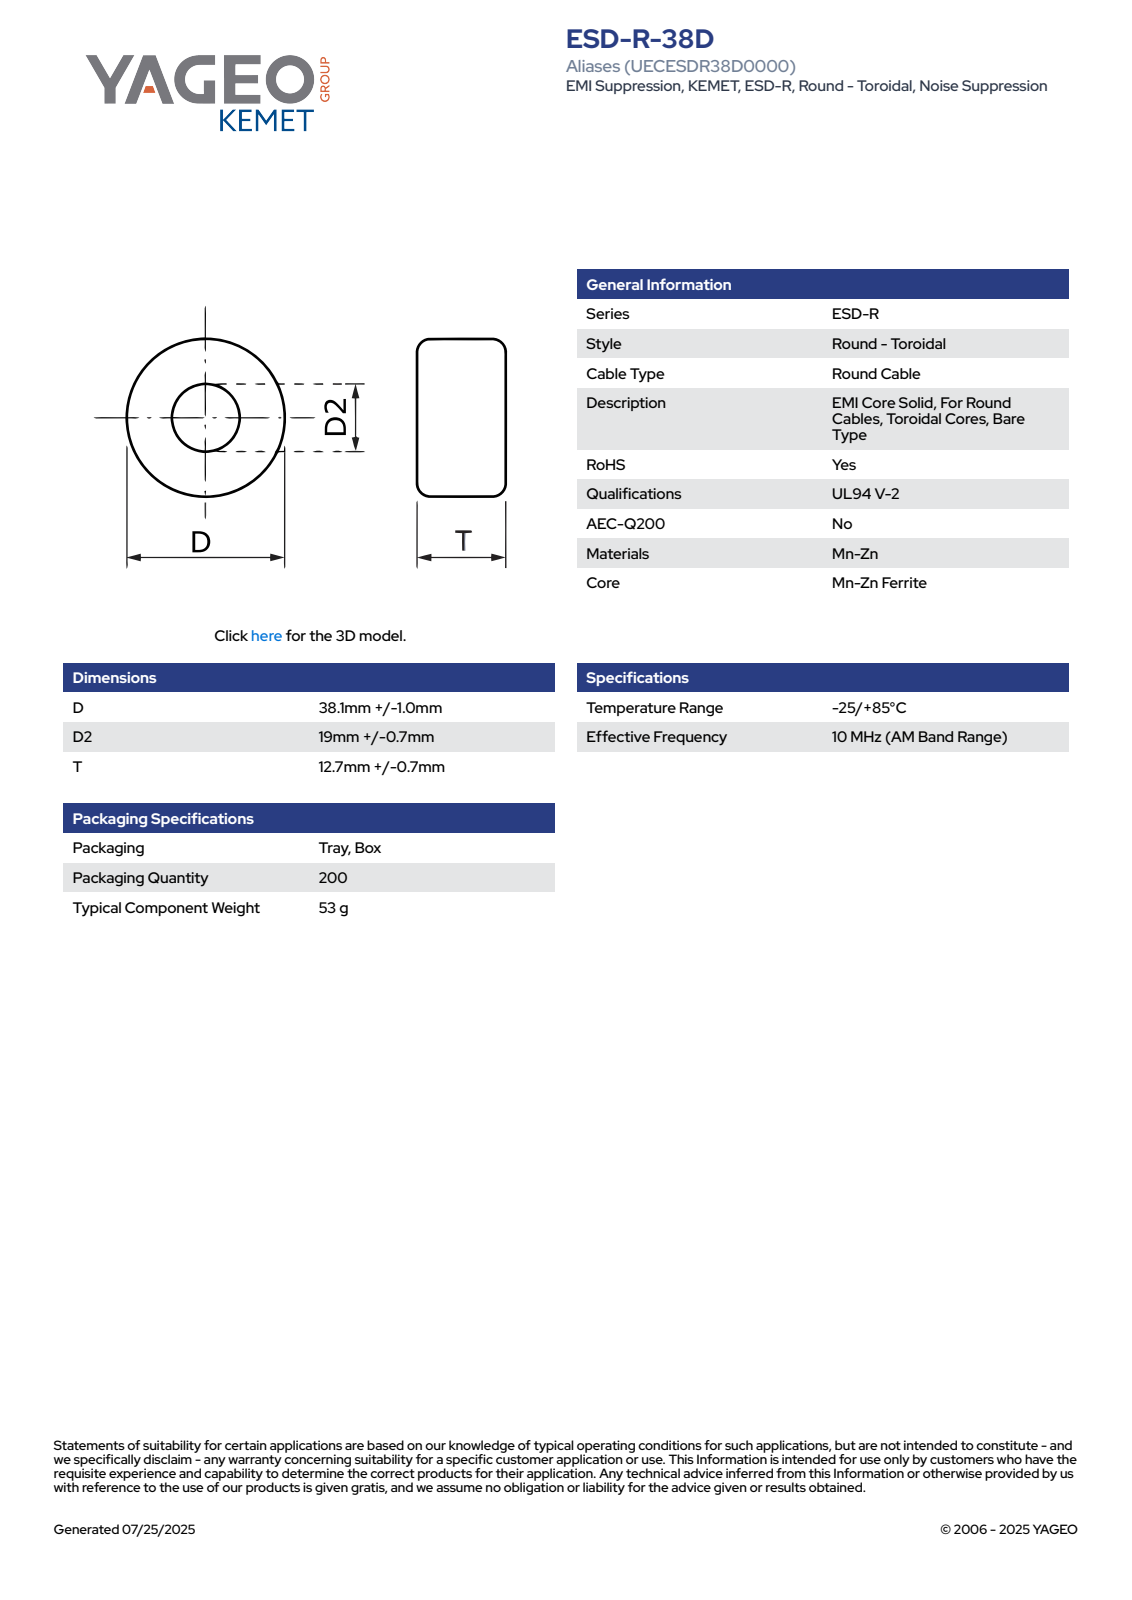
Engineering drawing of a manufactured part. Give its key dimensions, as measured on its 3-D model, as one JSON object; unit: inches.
{"part_name": "EC_KBC_D39.1D219T13.4", "step_written_by": "SolidWorks 2021 (AUTOMOTIVE_DESIGN)", "units": "inches", "bodies": {"solids": 1, "faces": 66, "planar": 24, "cylindrical": 7, "other": 35}, "overall_size": [1.54, 1.539, 0.528], "volume_in3": 0.745, "surface_area_in2": 6.453, "round_holes": [[0.748, 1]], "round_bosses_or_shafts": [[1.539, 1]], "partial_cylinders_radius": [[0.77, 1]], "face_to_face_distances": [0.528, 0.23, 0.297, 0.067, 0.013, 0.243, 0.285, 0.054, 0.042, 0.272]}
